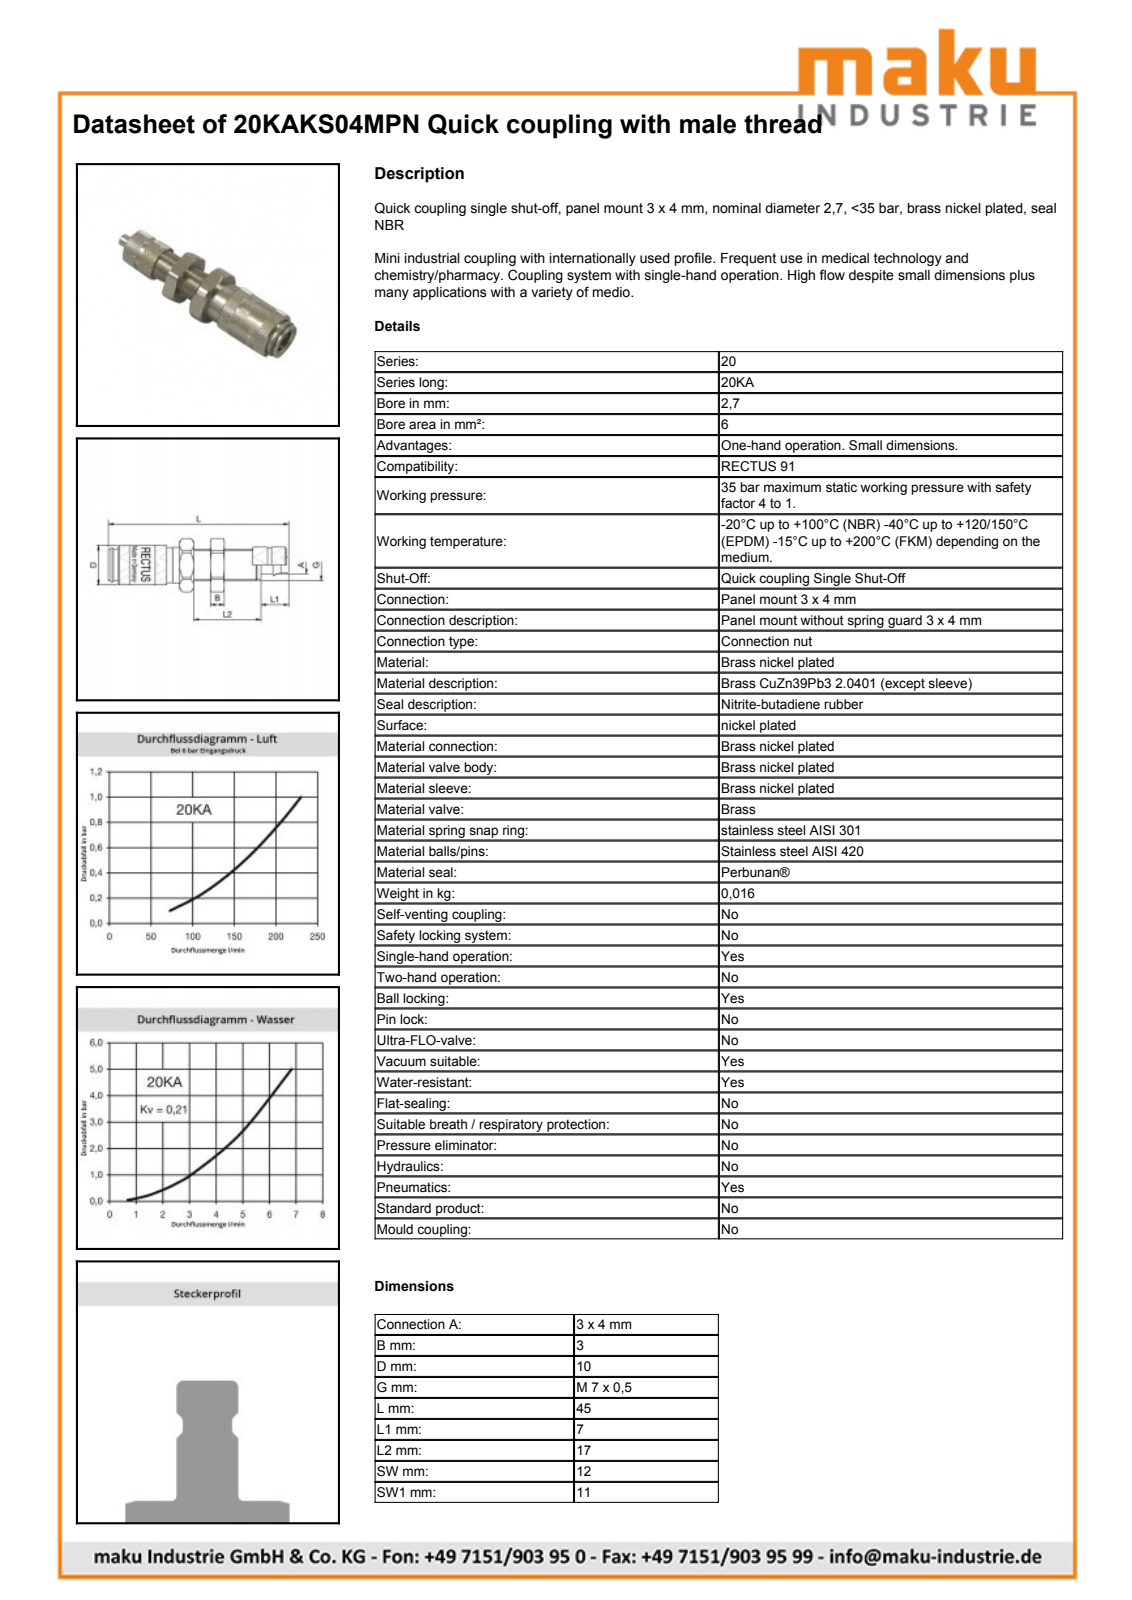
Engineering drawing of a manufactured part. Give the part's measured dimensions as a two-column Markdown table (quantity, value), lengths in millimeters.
| quantity | value |
| --- | --- |
| part name | D109386 |
| STEP written by | Autodesk Inventor 2013 (AUTOMOTIVE_DESIGN) |
| units | millimeters |
| bodies | 2 solids, 512 faces (174 planar, 85 cylindrical, 253 other) |
| overall size | 45.05 × 13 × 12.52 |
| volume | 2 628 mm³ |
| surface area | 3 042 mm² |
| round holes (diameter × count) | 4.25 × 1, 6.3 × 1, 6.45 × 1, 6.5 × 1, 7.46 × 1, 8.15 × 1, 9.15 × 1, 9.2 × 1 |
| round bosses / shafts (diameter × count) | 10.35 × 1, 10 × 1, 9 × 1, 8.9 × 1, 8.1 × 1, 8 × 1, 7.8 × 1, 7.7 × 1 |
| partial cylindrical surfaces (radius × count) | 4.9 × 1, 6.2 × 1, 6.5 × 1 |
| main face-to-face distances | 12.3, 9.3, 3.05, 18, 6.25, 11, 21.05, 9.25, 3, 27.3 |
